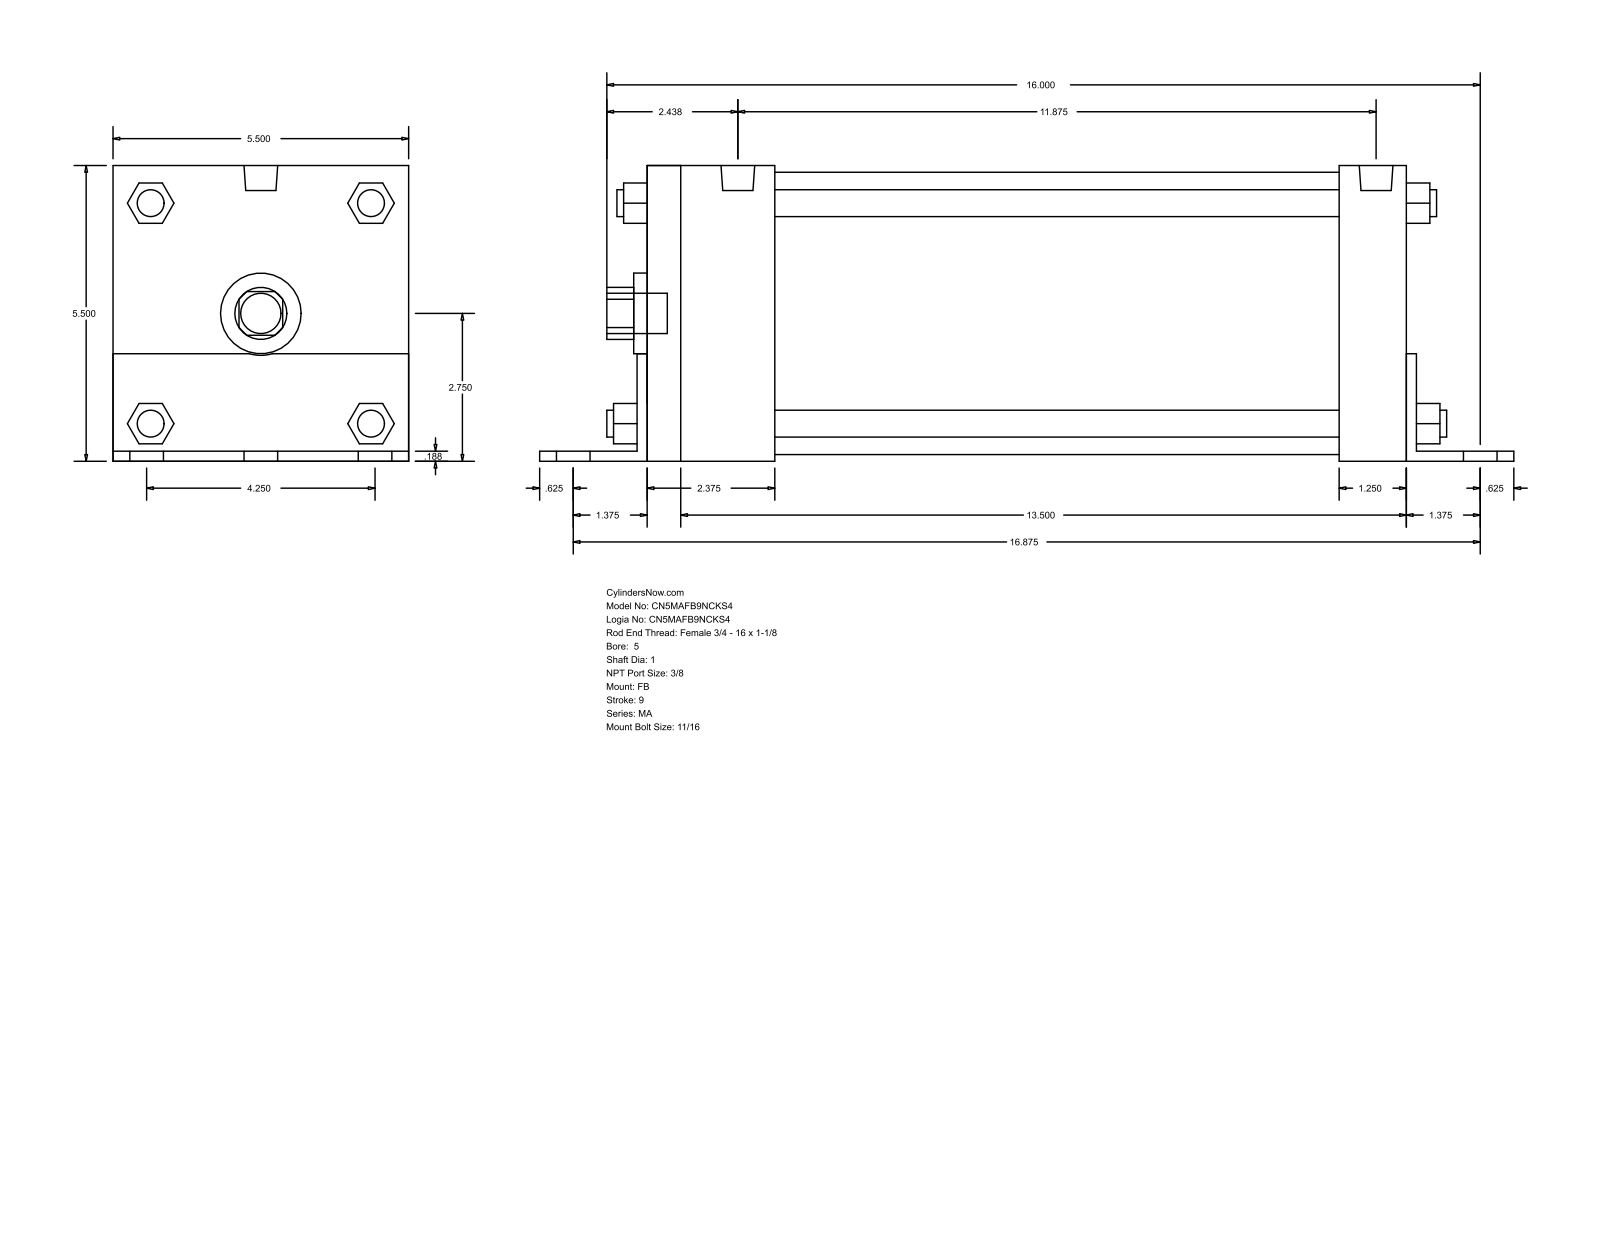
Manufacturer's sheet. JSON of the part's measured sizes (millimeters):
{"part_name": "MA_FB__0500_1", "step_written_by": "GSSL Pune (CONFIG_CONTROL_DESIGN)", "units": "millimeters", "bodies": {"solids": 0, "faces": 140, "planar": 105, "cylindrical": 35, "other": 0}, "overall_size": [460.38, 139.75, 139.7], "round_holes": [[25.4, 1], [38.1, 1], [133.35, 1]], "round_bosses_or_shafts": [[17.46, 6], [12.7, 4], [11.11, 4], [15.93, 2], [19.05, 1]], "partial_cylinders_radius": [[12.29, 1], [19.81, 1]], "face_to_face_distances": [139.7, 4.76, 139.75, 4.71, 134.99, 358.77, 4.77, 363.54, 363.53, 368.3]}
